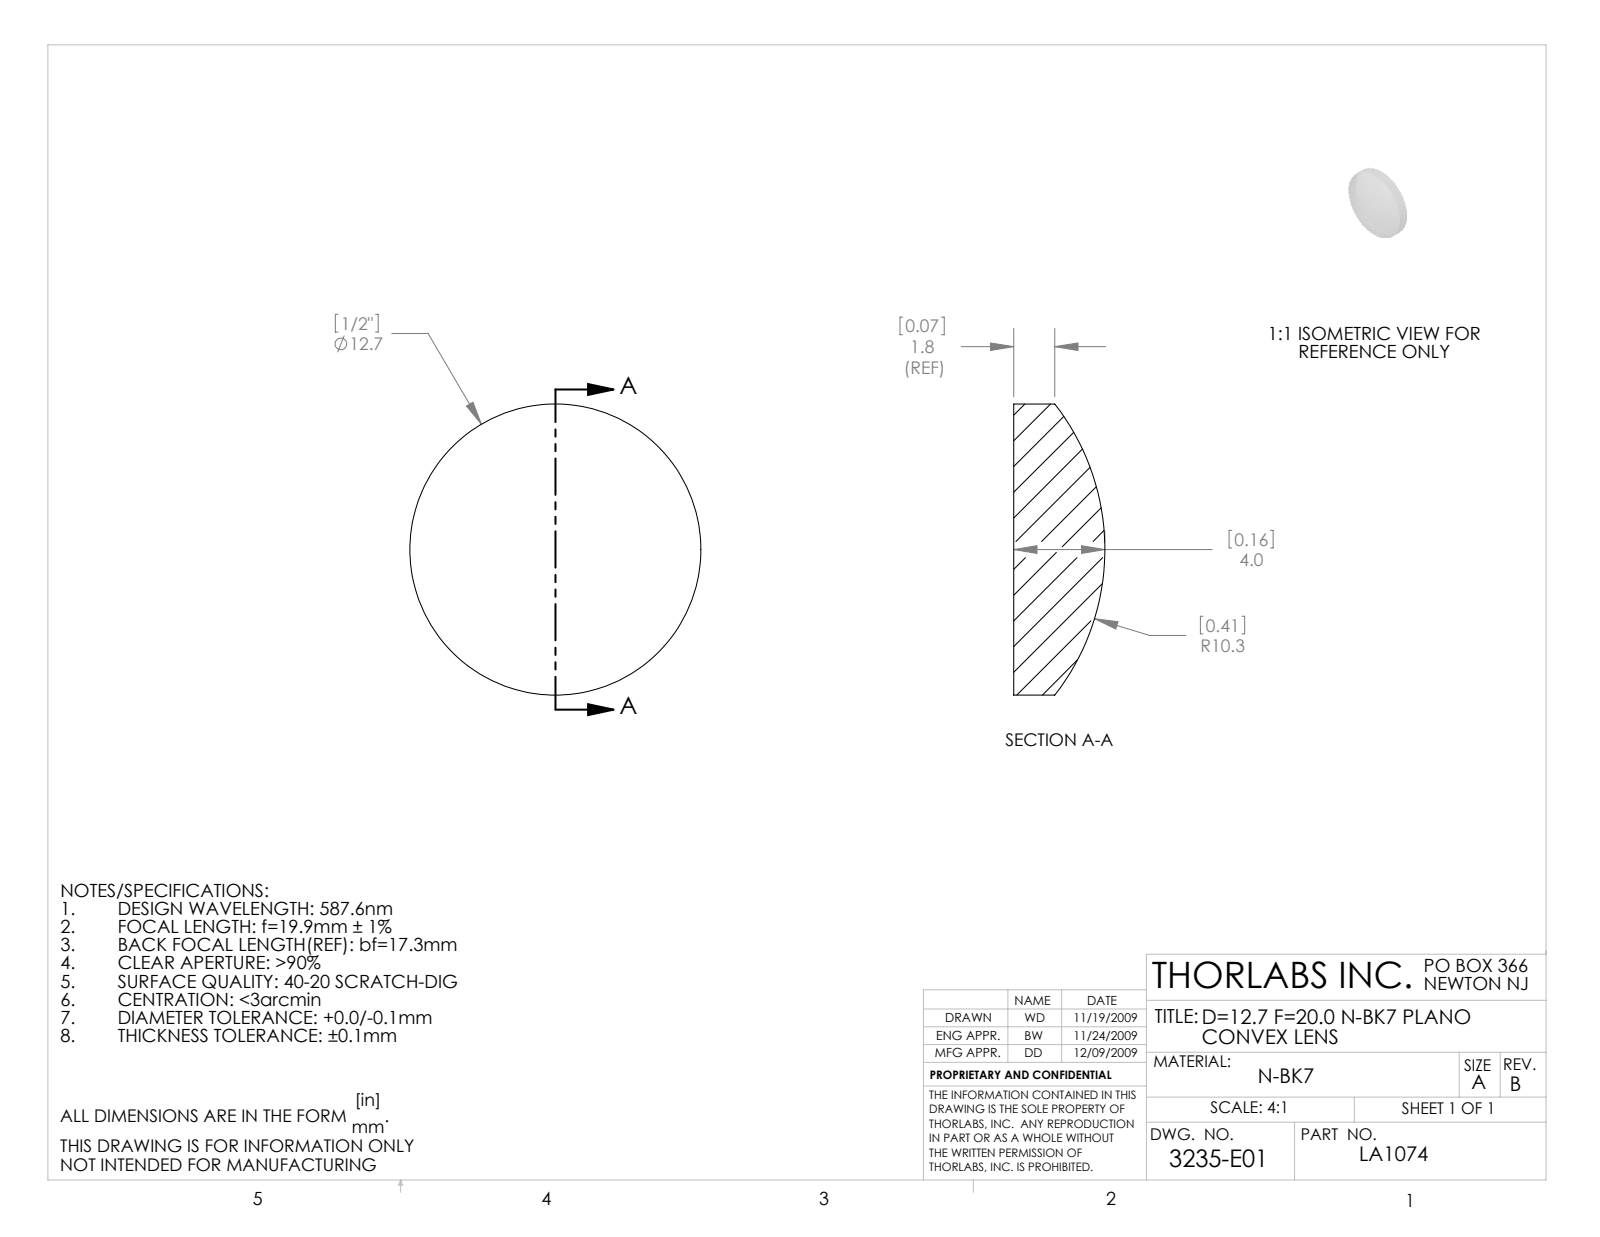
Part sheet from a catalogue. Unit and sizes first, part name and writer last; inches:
Units: inches
Overall size (bounding box): 0.5 × 0.5 × 0.157
Round bosses / shafts (diameter × count): ⌀0.5 ×1
Volume: 0.023 in³ · Surface area: 0.527 in²
Bodies: 1 solid, 5 faces (1 planar, 2 cylindrical, 2 other)
Part name (STEP PRODUCT): 3235-E0W
STEP written by: SolidWorks 2009 (AUTOMOTIVE_DESIGN)
